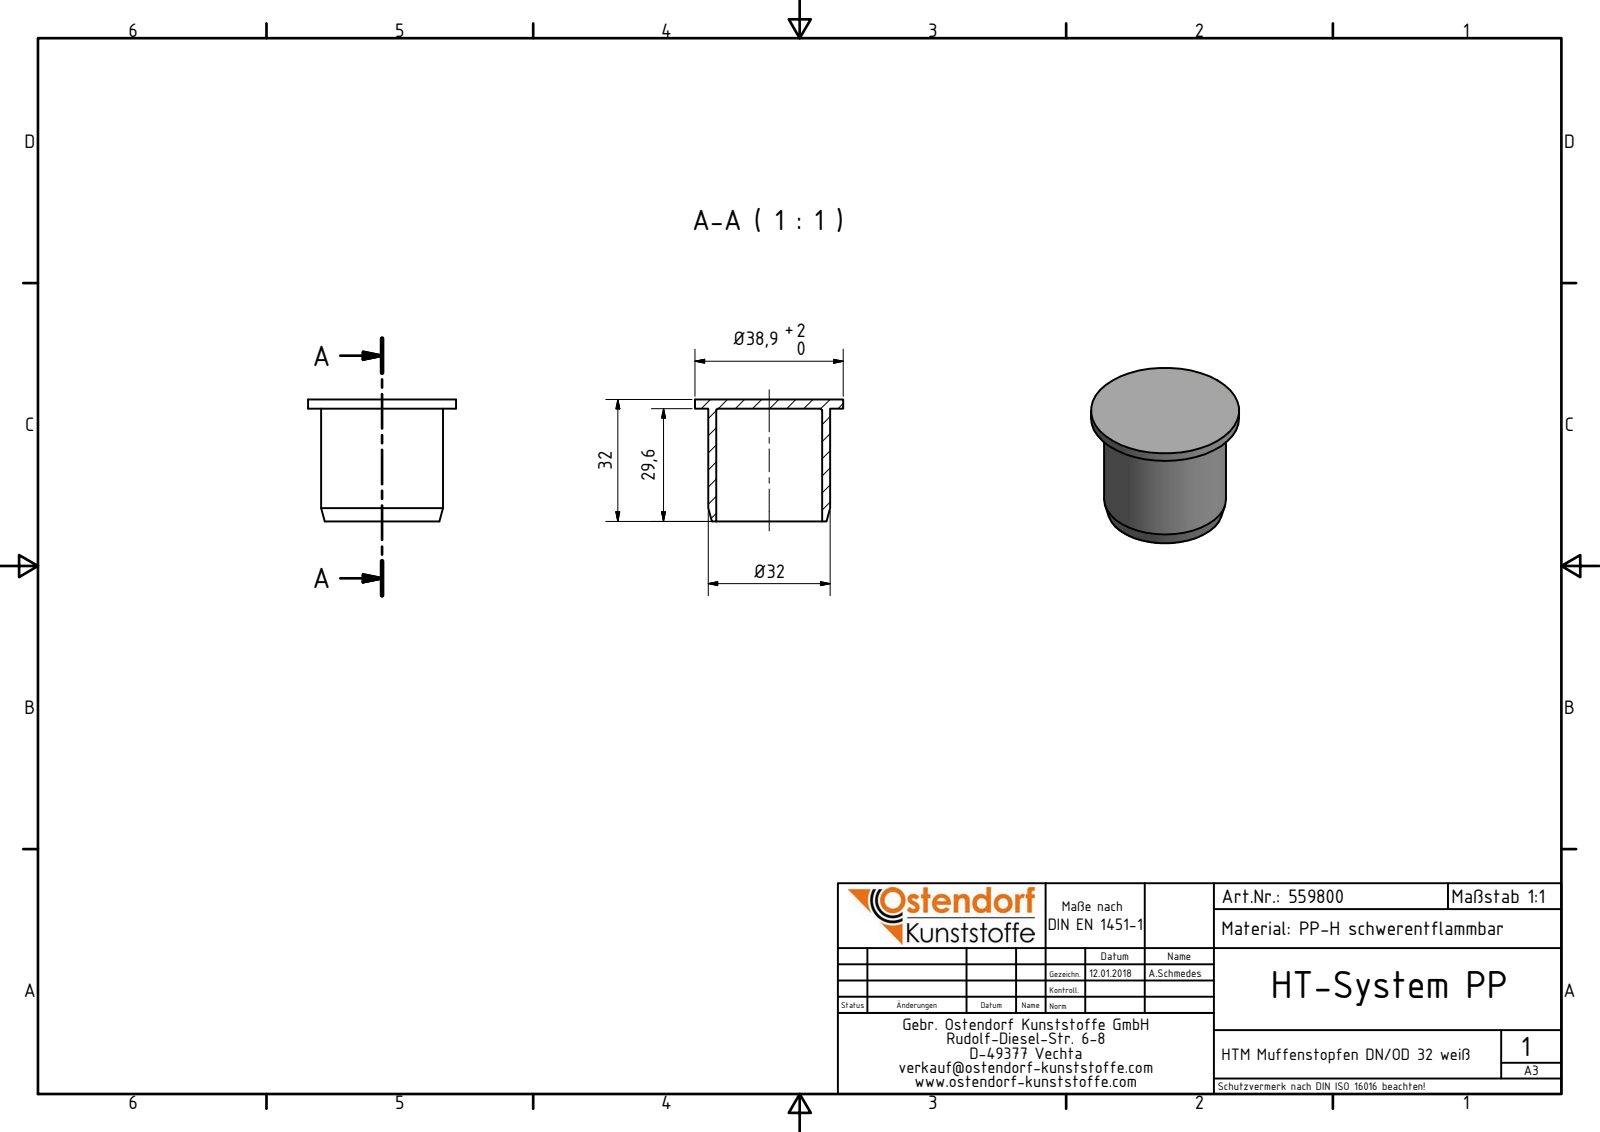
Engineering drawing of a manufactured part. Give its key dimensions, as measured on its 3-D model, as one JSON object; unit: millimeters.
{"part_name": "559800 HTM DN_OD 32 weiß", "step_written_by": "Autodesk Inventor 2016 (AUTOMOTIVE_DESIGN)", "units": "millimeters", "bodies": {"solids": 1, "faces": 9, "planar": 4, "cylindrical": 3, "other": 2}, "overall_size": [38.9, 38.9, 32], "volume_mm3": 8534, "surface_area_mm2": 8122, "round_holes": [[27.8, 1]], "round_bosses_or_shafts": [[38.9, 1], [32, 1]], "face_to_face_distances": [2.4, 29.6, 32]}
